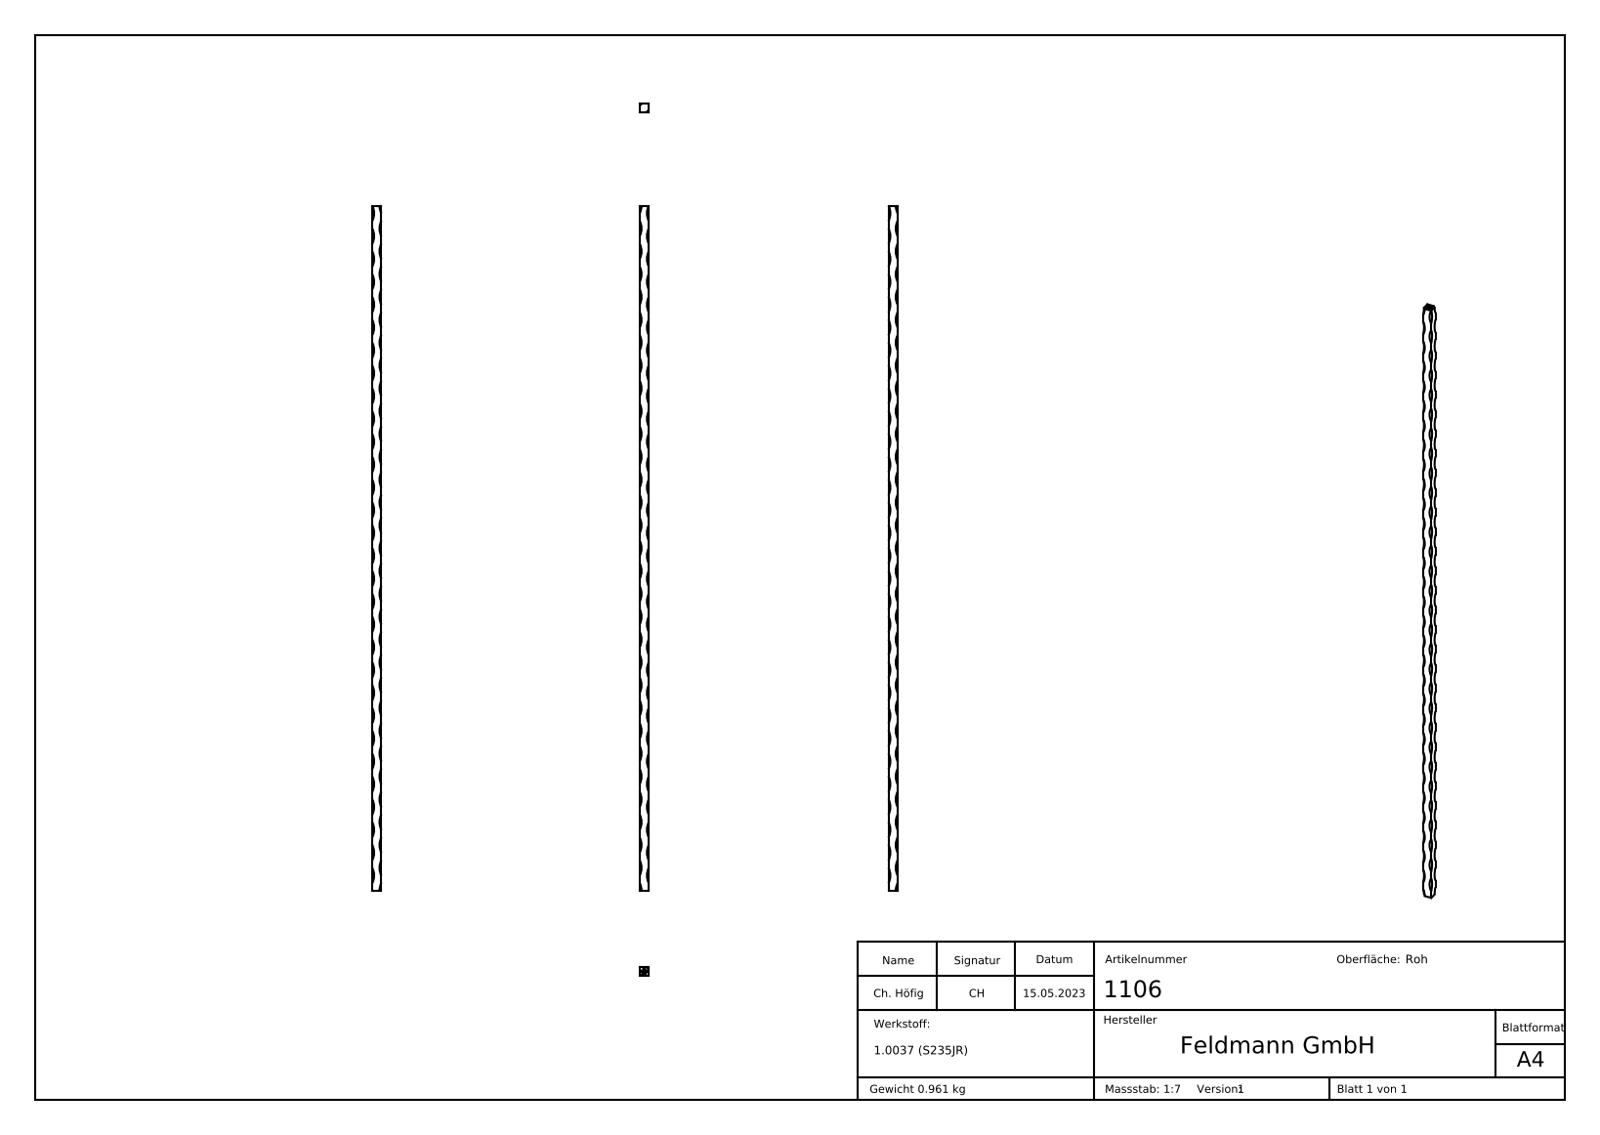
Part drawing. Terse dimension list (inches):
name: 1106
written by: SolidWorks 2018 (CONFIG_CONTROL_DESIGN)
unit: in
bodies: 1 solid, 323 faces (115 planar, 0 cylindrical, 208 other)
size: 35.433 × 0.472 × 0.472
volume: 7.518 in³; area: 64.94 in²
face distances: 0.472, 35.433, 35.429, 0.022, 0.018, 0.027, 0.045, 0.072, 0.045, 0.106
